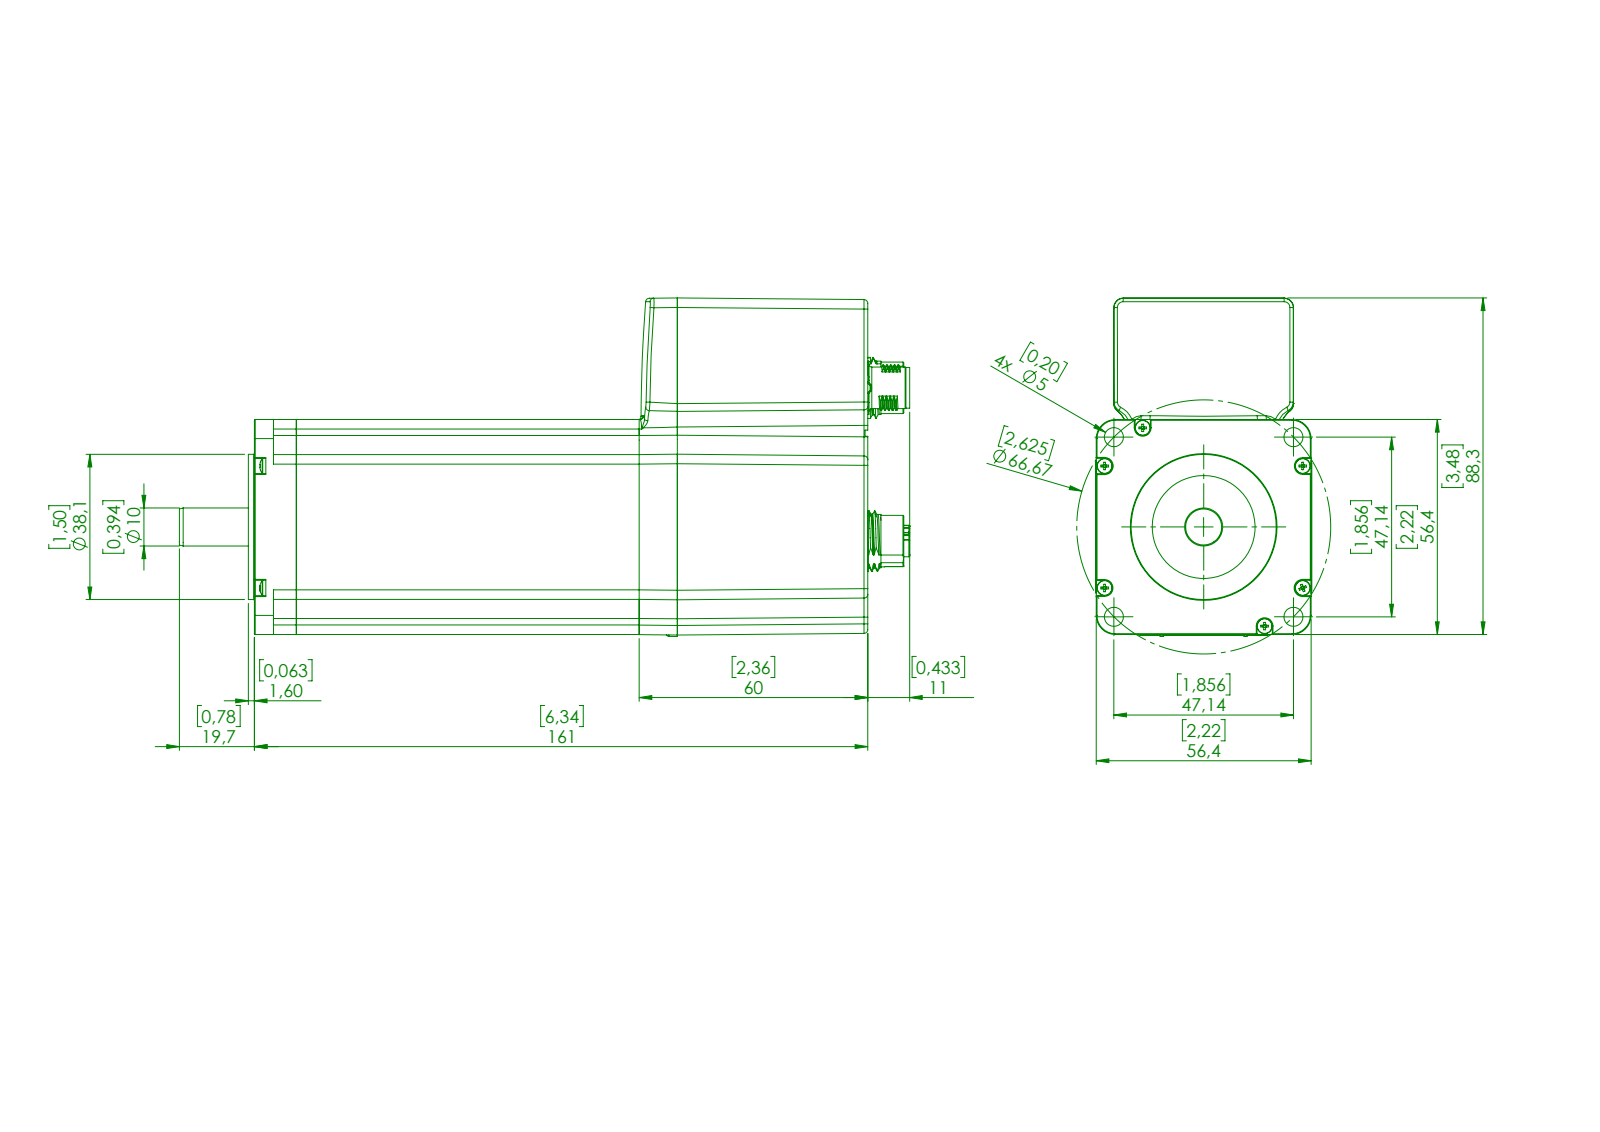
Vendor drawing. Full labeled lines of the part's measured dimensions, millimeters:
Part name (STEP PRODUCT): M12_17P_FEMALE_CHASSISLong; M12_4P_FEMALE_CHASSIS_ALTTYPELong; pan head cross recess screw_iso_ISO 7045 - M2 x 3 - Z - 3N; Front Cap MIS23X SOLID (+8 more)
STEP written by: SolidWorks 2016 (CONFIG_CONTROL_DESIGN)
Units: millimetres
Bodies: 16 solids, 2517 faces (874 planar, 734 cylindrical, 909 other)
Overall size (bounding box): 191.7 × 88.83 × 56.67
Volume: 557 395 mm³ · Surface area: 80 334 mm²
Round holes (diameter × count): ⌀1 ×27, ⌀2 ×6, ⌀2.5 ×6, ⌀5 ×4, ⌀12.2 ×3, ⌀1.52 ×2, ⌀8.6 ×2, ⌀11.13 ×2, ⌀14.6 ×2, ⌀3.3 ×1, ⌀4 ×1, ⌀8.3 ×1
Round bosses / shafts (diameter × count): ⌀1.1 ×17, ⌀0.6 ×17, ⌀1.6 ×13, ⌀1 ×7, ⌀4 ×5, ⌀13.25 ×4, ⌀13.5 ×3, ⌀0.22 ×3
Partial cylindrical surfaces — rounded edges, fillets, slot ends (radius × count): R0.2 ×64, R0.1 ×32, R2.5 ×29, R5 ×18, R1 ×16, R0.8 ×12, R0.15 ×10, R0.25 ×8
Main face-to-face distances: 56.4, 10, 100, 90, 49.3, 59.3, 149.3, 4.75, 11, 160.3
Hole centre spacings: 2.5, 3.54, 39.64, 0.62, 7.78, 7.95, 30, 30.53
